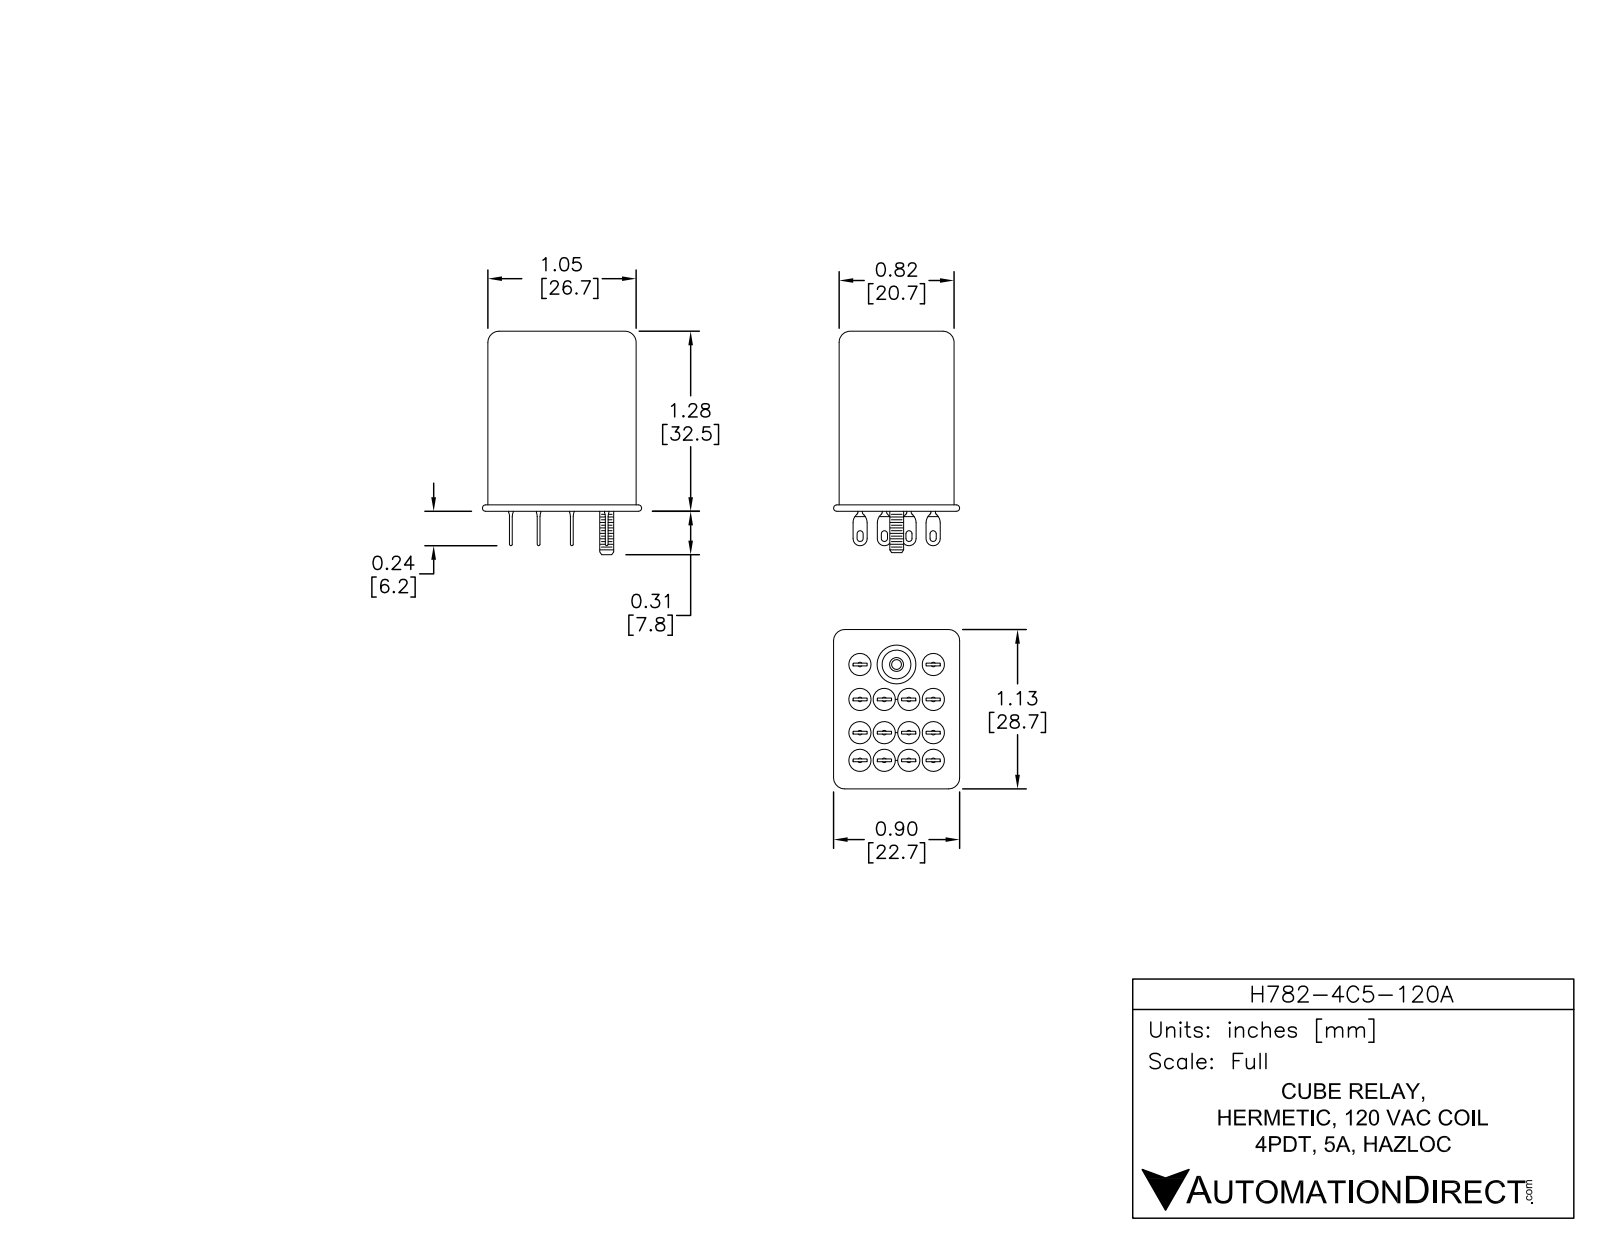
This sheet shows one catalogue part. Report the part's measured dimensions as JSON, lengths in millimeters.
{"part_name": "H782-4C5-120A", "step_written_by": "SolidWorks 2013 (AUTOMOTIVE_DESIGN)", "units": "millimeters", "bodies": {"solids": 2, "faces": 408, "planar": 186, "cylindrical": 178, "other": 44}, "overall_size": [35.12, 28.8, 22.9], "volume_mm3": 15264, "surface_area_mm2": 4133, "round_holes": [[6, 1]], "round_bosses_or_shafts": [[3.15, 14], [2.4, 1]], "partial_cylinders_radius": [[0.1, 56], [0.5, 36], [0.2, 8], [2, 4]], "face_to_face_distances": [20.5, 27.6, 26.5, 27.62, 5.2, 0.4, 10.4, 10, 4.8, 5.6]}
